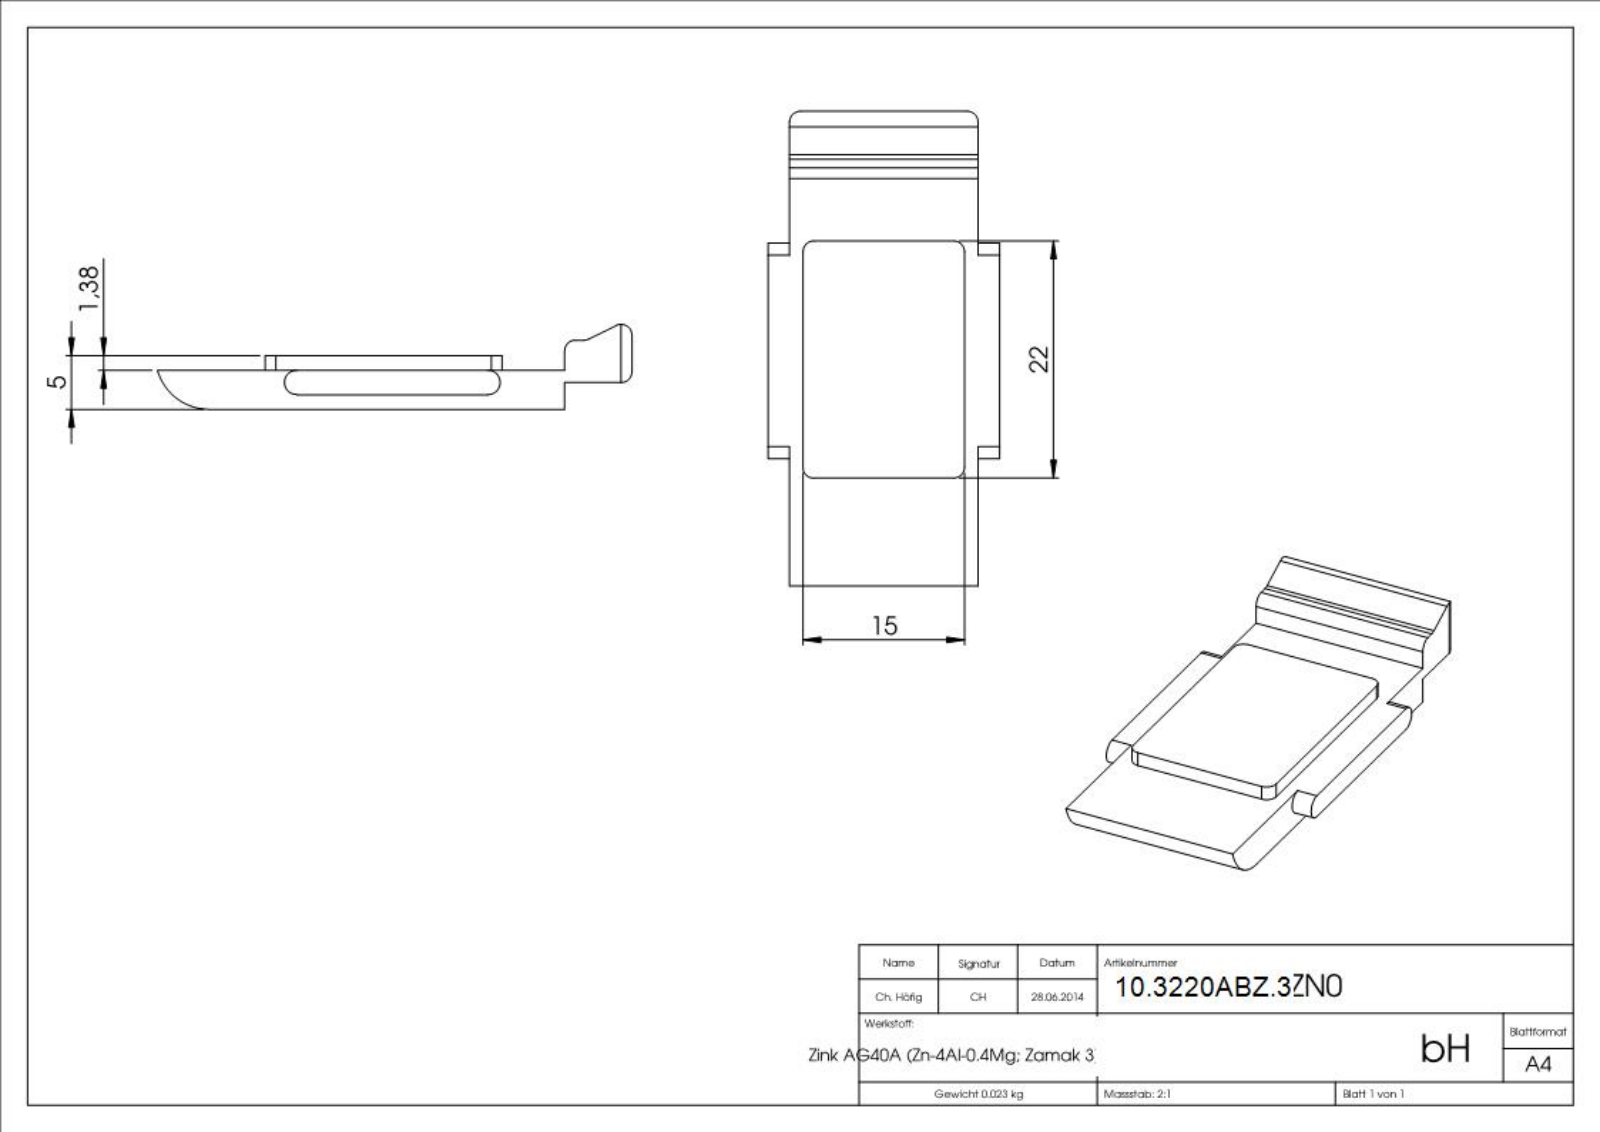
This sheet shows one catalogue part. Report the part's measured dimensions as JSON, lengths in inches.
{"part_name": "35-Boden-GU_35-Boden-GU; 35-BODEN-ZN0; 35-Boden; 35-Boden-GU (+1 more)", "step_written_by": "SolidWorks 2018 (CONFIG_CONTROL_DESIGN)", "units": "inches", "bodies": {"solids": 2, "faces": 325, "planar": 182, "cylindrical": 23, "other": 120}, "overall_size": [1.742, 0.843, 0.308], "volume_in3": 0.208, "surface_area_in2": 4.476, "partial_cylinders_radius": [[0.039, 14], [0.197, 9]], "face_to_face_distances": [0.02, 0.157, 0.197, 0.039, 0.177, 0.685, 0.015, 0.143, 0.034, 0.054]}
